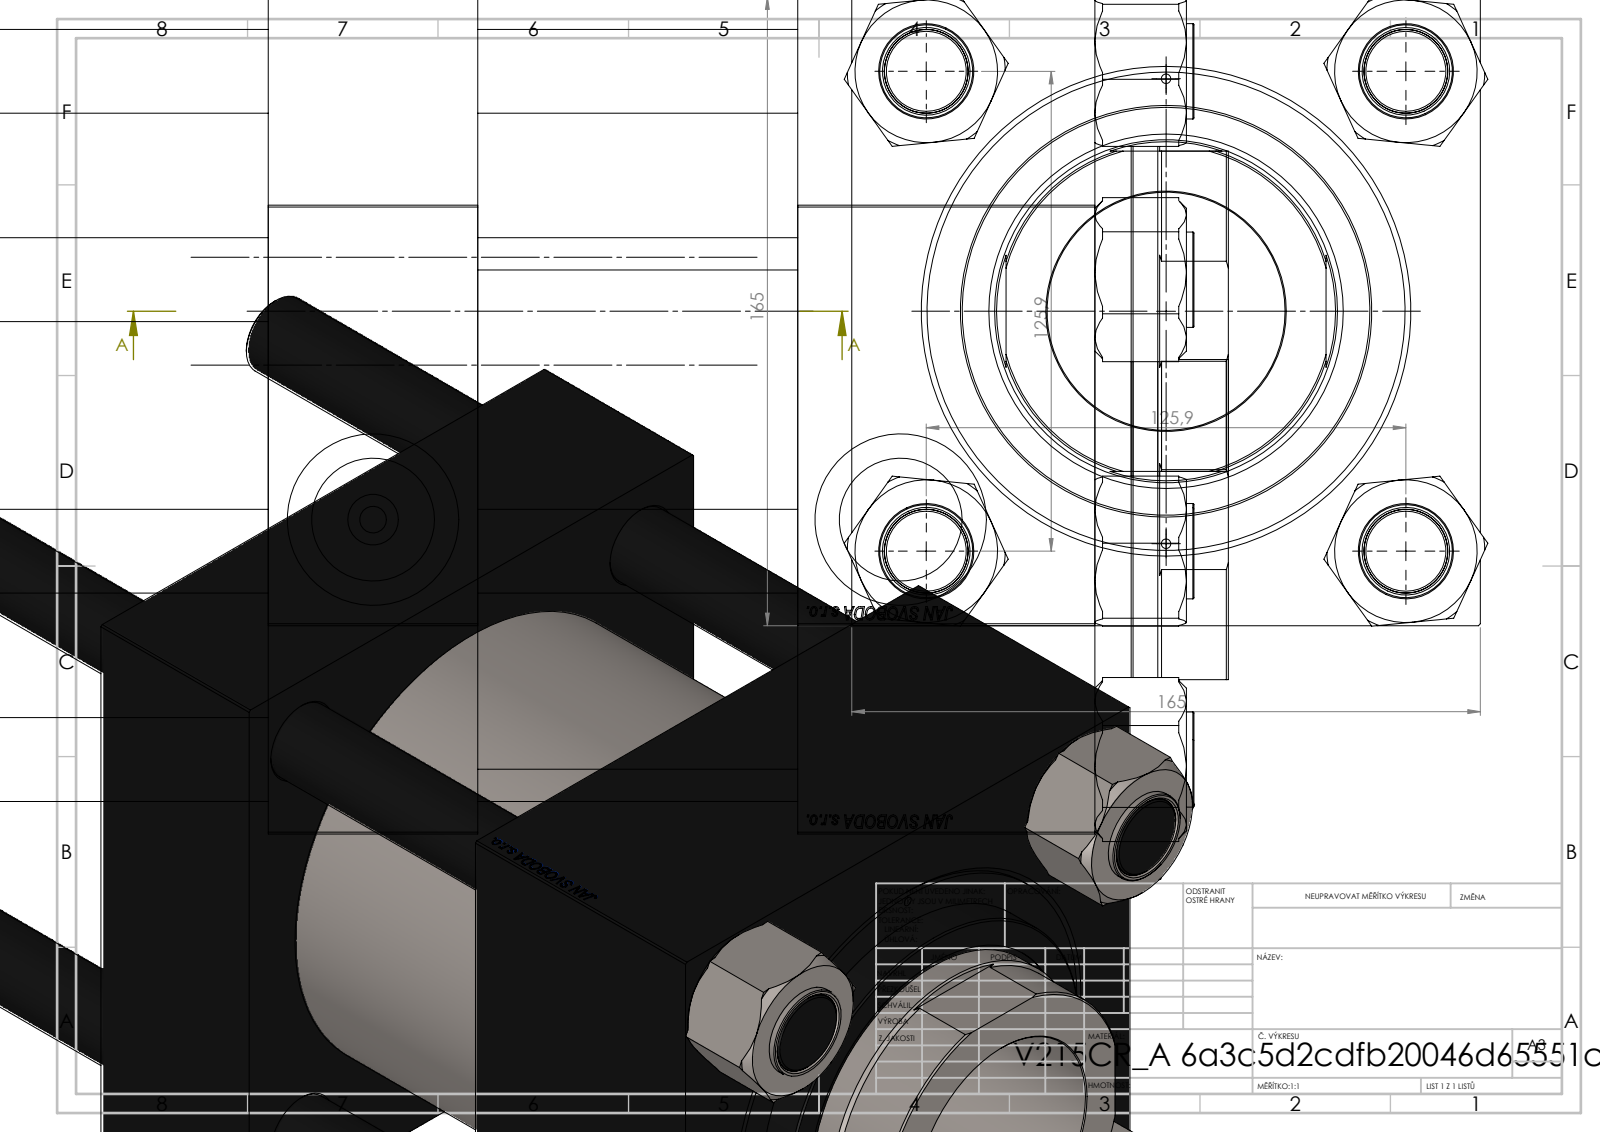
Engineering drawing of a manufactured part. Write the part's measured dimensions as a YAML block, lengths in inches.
part_name: "V215CR_BODY_A; NUT_M5; V215_VC_A; V215CR_VCP (+1 more)"
step_written_by: "SolidWorks 2019 (CONFIG_CONTROL_DESIGN)"
units: inches
bodies: {solids: 11, faces: 1188, planar: 570, cylindrical: 82, other: 536}
overall_size: [13.11, 6.651, 6.507]
volume: 298
surface_area: 884.2
round_holes:
  - {diameter: 0.866, count: 4}
  - {diameter: 0.098, count: 2}
  - {diameter: 0.276, count: 2}
  - {diameter: 1.269, count: 2}
  - {diameter: 1.772, count: 2}
  - {diameter: 2.461, count: 1}
  - {diameter: 3.543, count: 1}
  - {diameter: 3.661, count: 1}
  - {diameter: 3.78, count: 1}
  - {diameter: 4.921, count: 1}
  - {diameter: 4.941, count: 1}
round_bosses_or_shafts:
  - {diameter: 0.984, count: 4}
  - {diameter: 5.157, count: 1}
  - {diameter: 4.252, count: 1}
partial_cylinders:
  - {radius: 1.732, count: 1}
face_to_face_distances: [6.496, 2.165, 6.378, 8.543, 3.307, 5.472, 3.071, 7.413, 5.248, 1.941]
hole_center_spacings: [2.48, 3.505, 4.957, 5.473, 2.402, 7.01, 4.803, 5.453]
